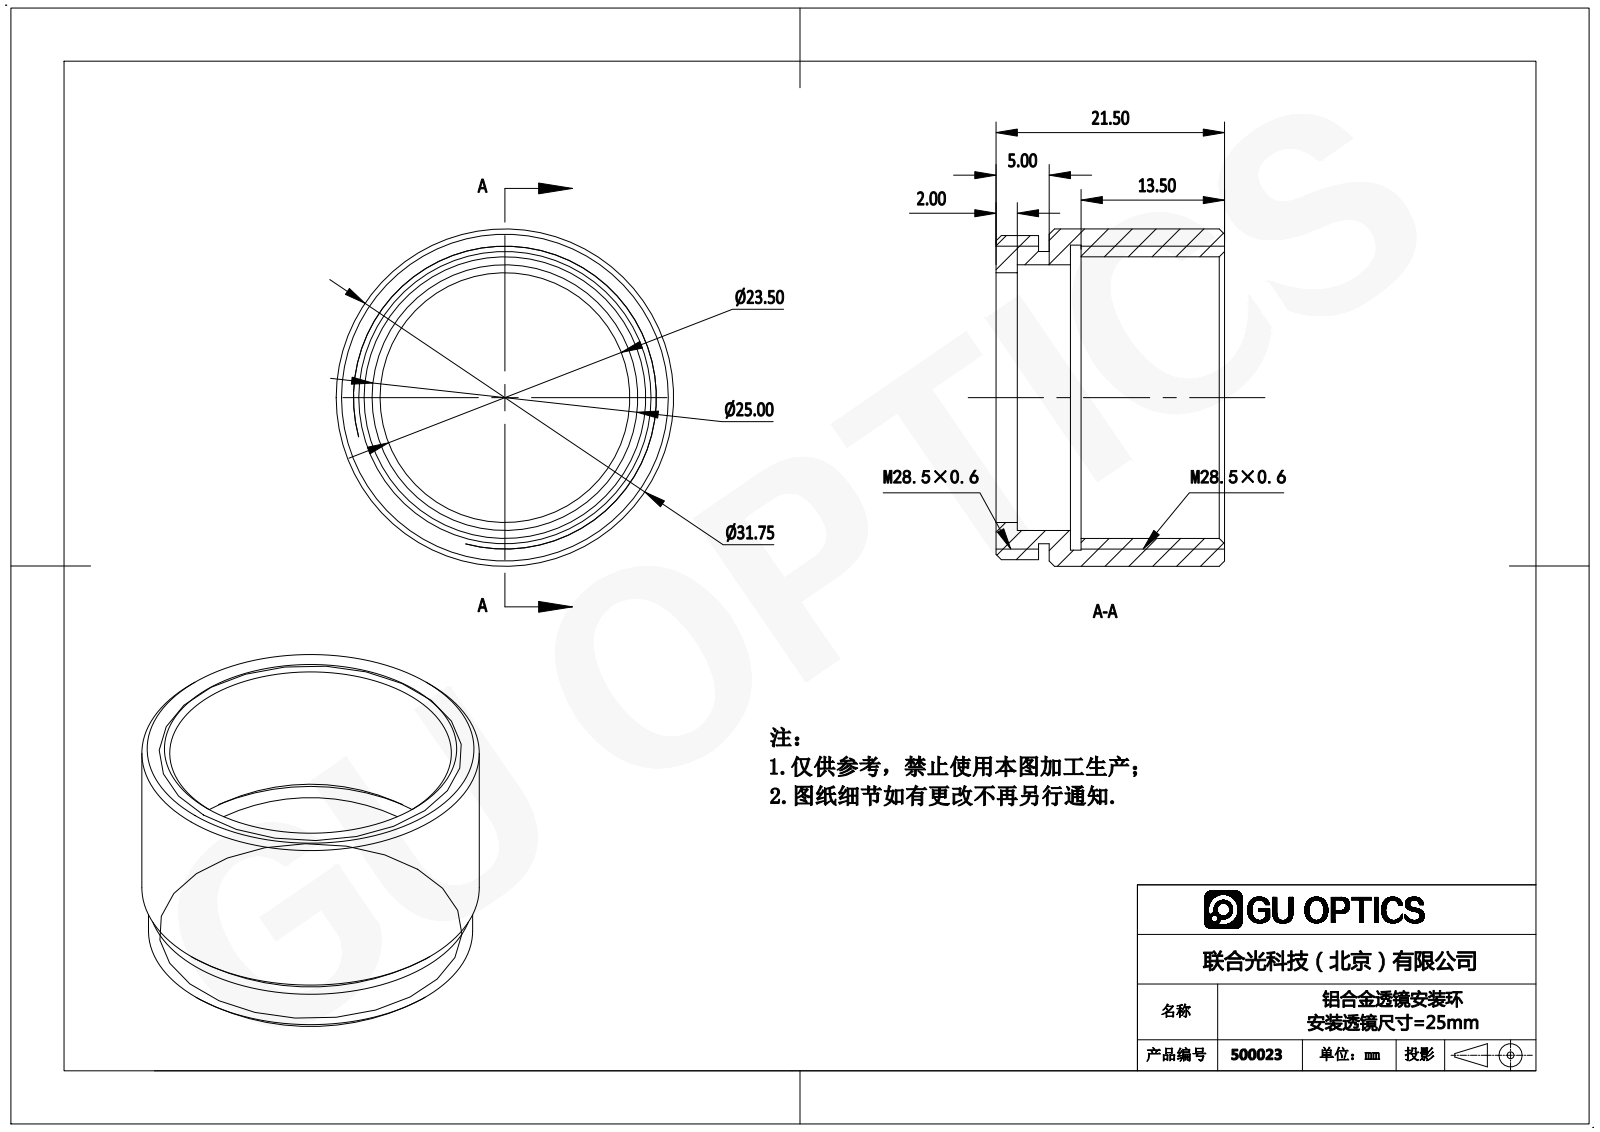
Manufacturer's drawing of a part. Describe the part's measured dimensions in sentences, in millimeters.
The part is named "500023". Its 3-D file was written by "SolidWorks 2016 (AUTOMOTIVE_DESIGN)". It is 1 solid with 29 faces: 7 planar, 14 cylindrical and 8 other. Overall it measures 31.75 by 31.75 by 21.5 millimeters. Its volume is 5 118 cubic millimeters and its surface area 4 938 square millimeters. Round holes: 1 of diameter 23.5, 1 of diameter 25, 1 of diameter 26.5, 1 of diameter 28.7. Round bosses or shafts: 1 of diameter 31.75, 1 of diameter 30.5, 1 of diameter 27.5. The main face-to-face distances are 3, 2, 4, 1, 5, 7, 21.5, 14.5, 16.5, 17.5.
